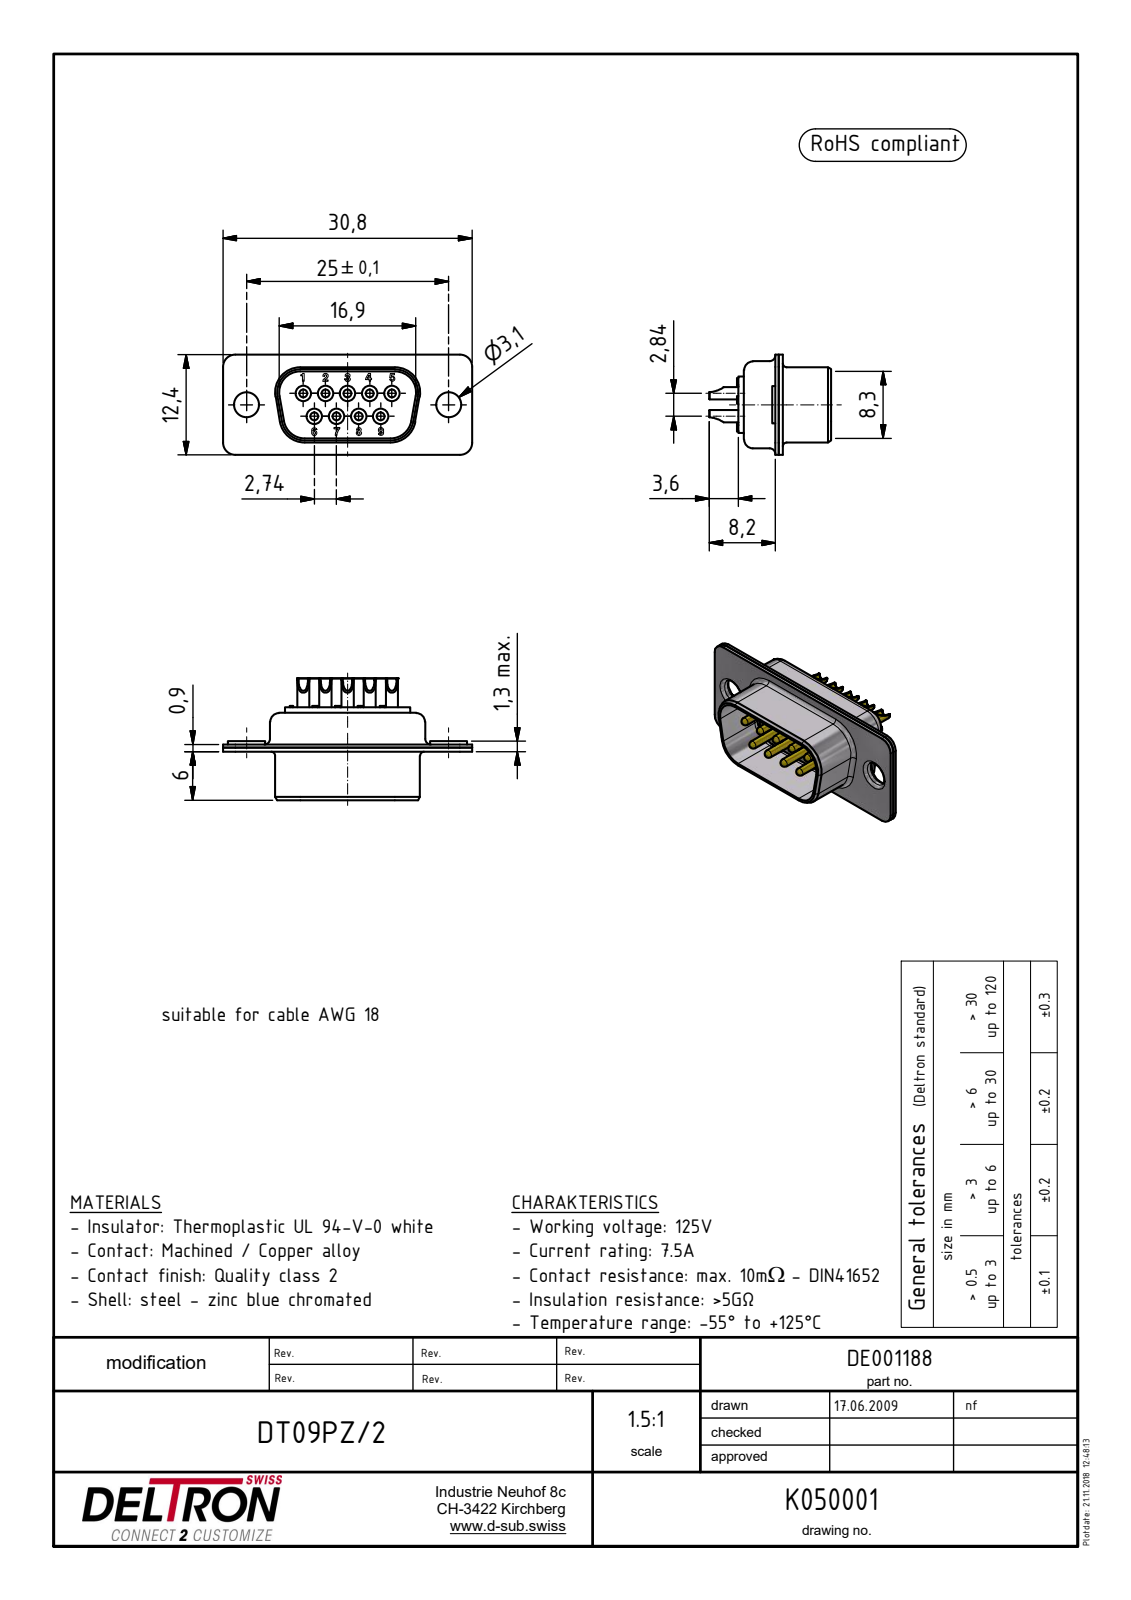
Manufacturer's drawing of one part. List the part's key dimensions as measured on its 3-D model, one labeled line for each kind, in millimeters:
Part name (STEP PRODUCT): N00401_BG; R+B00919_BG; R+B00142_BG; R+B00135_BG (+1 more)
STEP written by: Autodesk Inventor 2015 (AUTOMOTIVE_DESIGN)
Units: millimetres
Bodies: 12 solids, 590 faces (262 planar, 199 cylindrical, 129 other)
Overall size (bounding box): 30.8 × 15.1 × 12.4
Volume: 1 167 mm³ · Surface area: 3 473 mm²
Round holes (diameter × count): ⌀1.2 ×9, ⌀1.92 ×9, ⌀2.3 ×9, ⌀0.24 ×2, ⌀0.28 ×2, ⌀0.34 ×2, ⌀3.1 ×2, ⌀4.06 ×2
Round bosses / shafts (diameter × count): ⌀2.23 ×9, ⌀1.96 ×9, ⌀1.94 ×9, ⌀1.6 ×9, ⌀1.6 ×9, ⌀1.5 ×9, ⌀1 ×9, ⌀4.6 ×2
Partial cylindrical surfaces — rounded edges, fillets, slot ends (radius × count): R2 ×12, R0.7 ×8, R1 ×8, R1.1 ×8, R0.5 ×4, R1.2 ×4, R1.5 ×4, R1.6 ×4
Main face-to-face distances: 0.5, 0.4, 0.9, 8.8, 0.65, 0.8, 8.3, 0.6, 8.95, 9.45
Hole centre spacings: 3.15, 2.74, 5, 5.48, 7.42, 7.16, 8.22, 0.41
